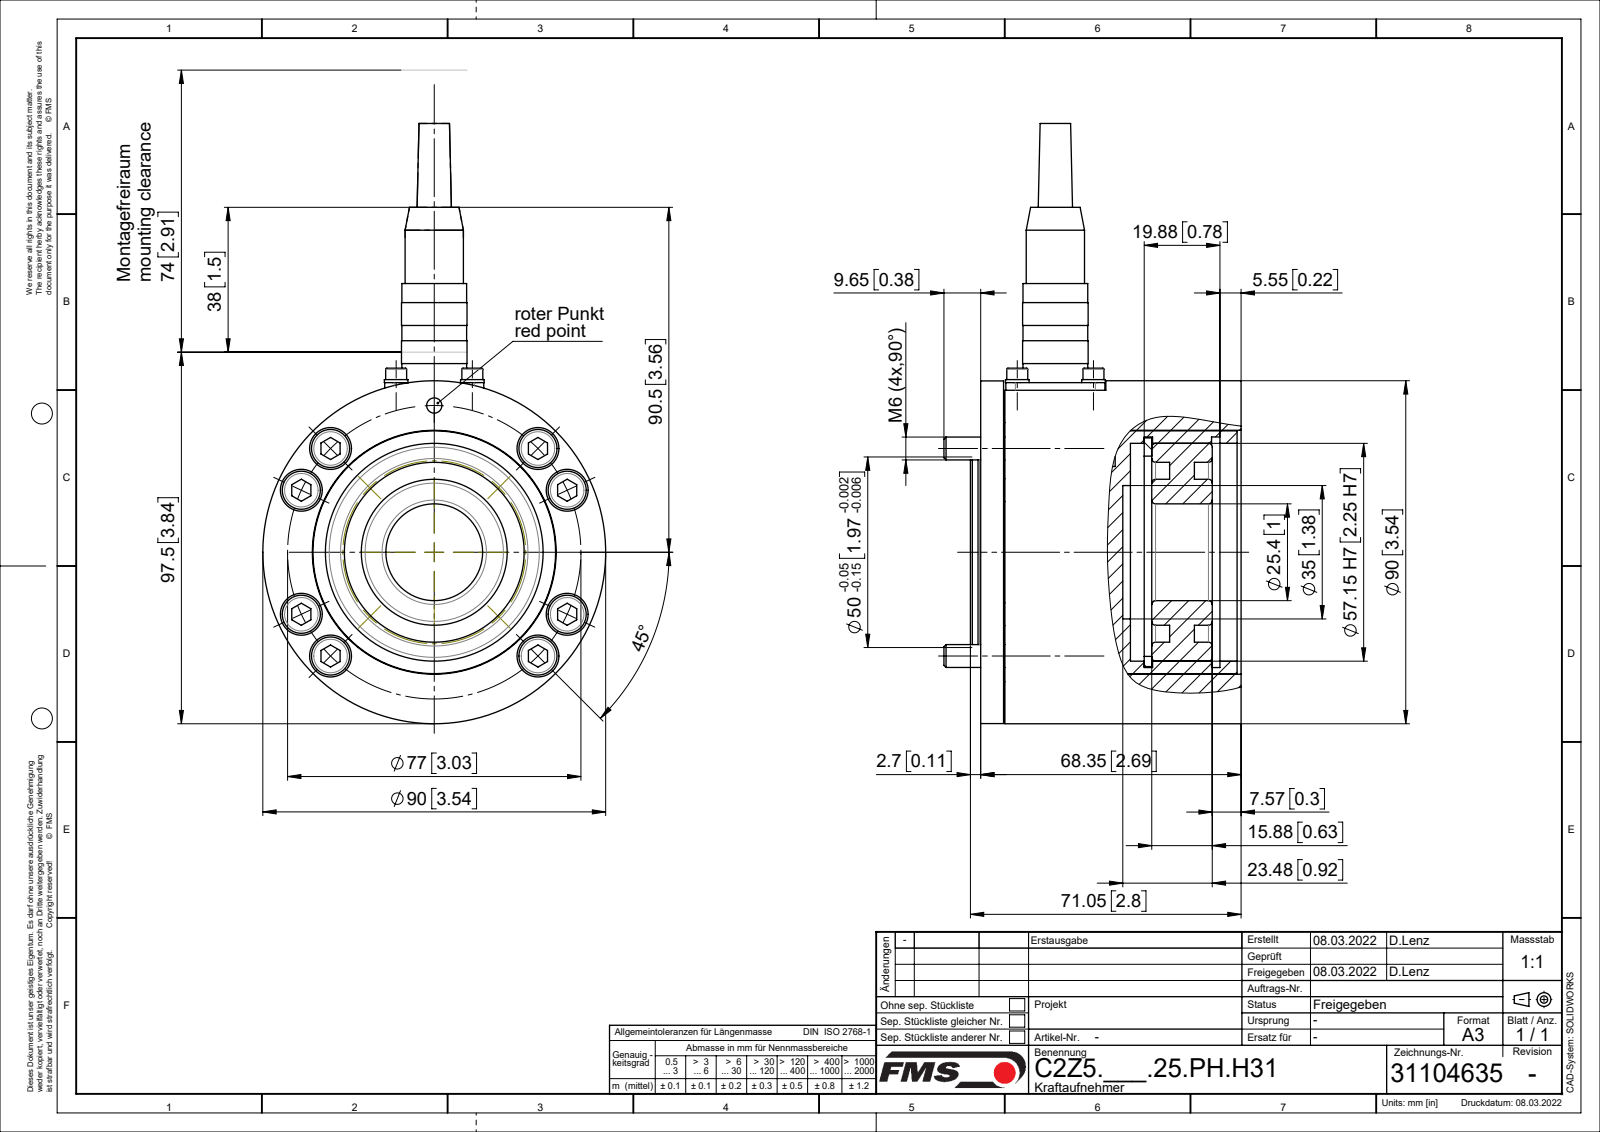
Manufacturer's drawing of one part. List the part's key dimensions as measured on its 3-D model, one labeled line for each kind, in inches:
Part name (STEP PRODUCT): Zyl-Schr DIN912_M6x40; 31104635; 31104498_stp_nach_Vergueten; Kabeldose_M14x1_Mini_5pol (+8 more)
STEP written by: SolidWorks 2018 (CONFIG_CONTROL_DESIGN)
Units: inches
Bodies: 23 solids, 578 faces (206 planar, 258 cylindrical, 114 other)
Overall size (bounding box): 6.201 × 3.543 × 3.071
Volume: 18.61 in³ · Surface area: 187.6 in²
Round holes (diameter × count): ⌀0.256 ×8, ⌀0.433 ×8, ⌀0.098 ×6, ⌀0.122 ×4, ⌀0.126 ×4, ⌀0.197 ×4, ⌀0.276 ×4, ⌀0.157 ×2, ⌀0.402 ×1, ⌀0.472 ×1, ⌀0.591 ×1, ⌀0.709 ×1
Round bosses / shafts (diameter × count): ⌀0.394 ×8, ⌀0.236 ×8, ⌀0.059 ×5, ⌀0.244 ×4, ⌀0.217 ×4, ⌀0.118 ×4, ⌀3.543 ×1, ⌀3.539 ×1
Partial cylindrical surfaces — rounded edges, fillets, slot ends (radius × count): R0.004 ×4, R0.098 ×4, R0.164 ×2, R0.197 ×2, R0.913 ×1, R1.035 ×1
Main face-to-face distances: 0.236, 0.13, 0.106, 1.301, 1.26, 0.079, 1.496, 1.181, 1.154, 1.39
Hole centre spacings: 0.787, 1.516, 0.526, 0.557, 1.515, 1.739, 2.143, 2.483
